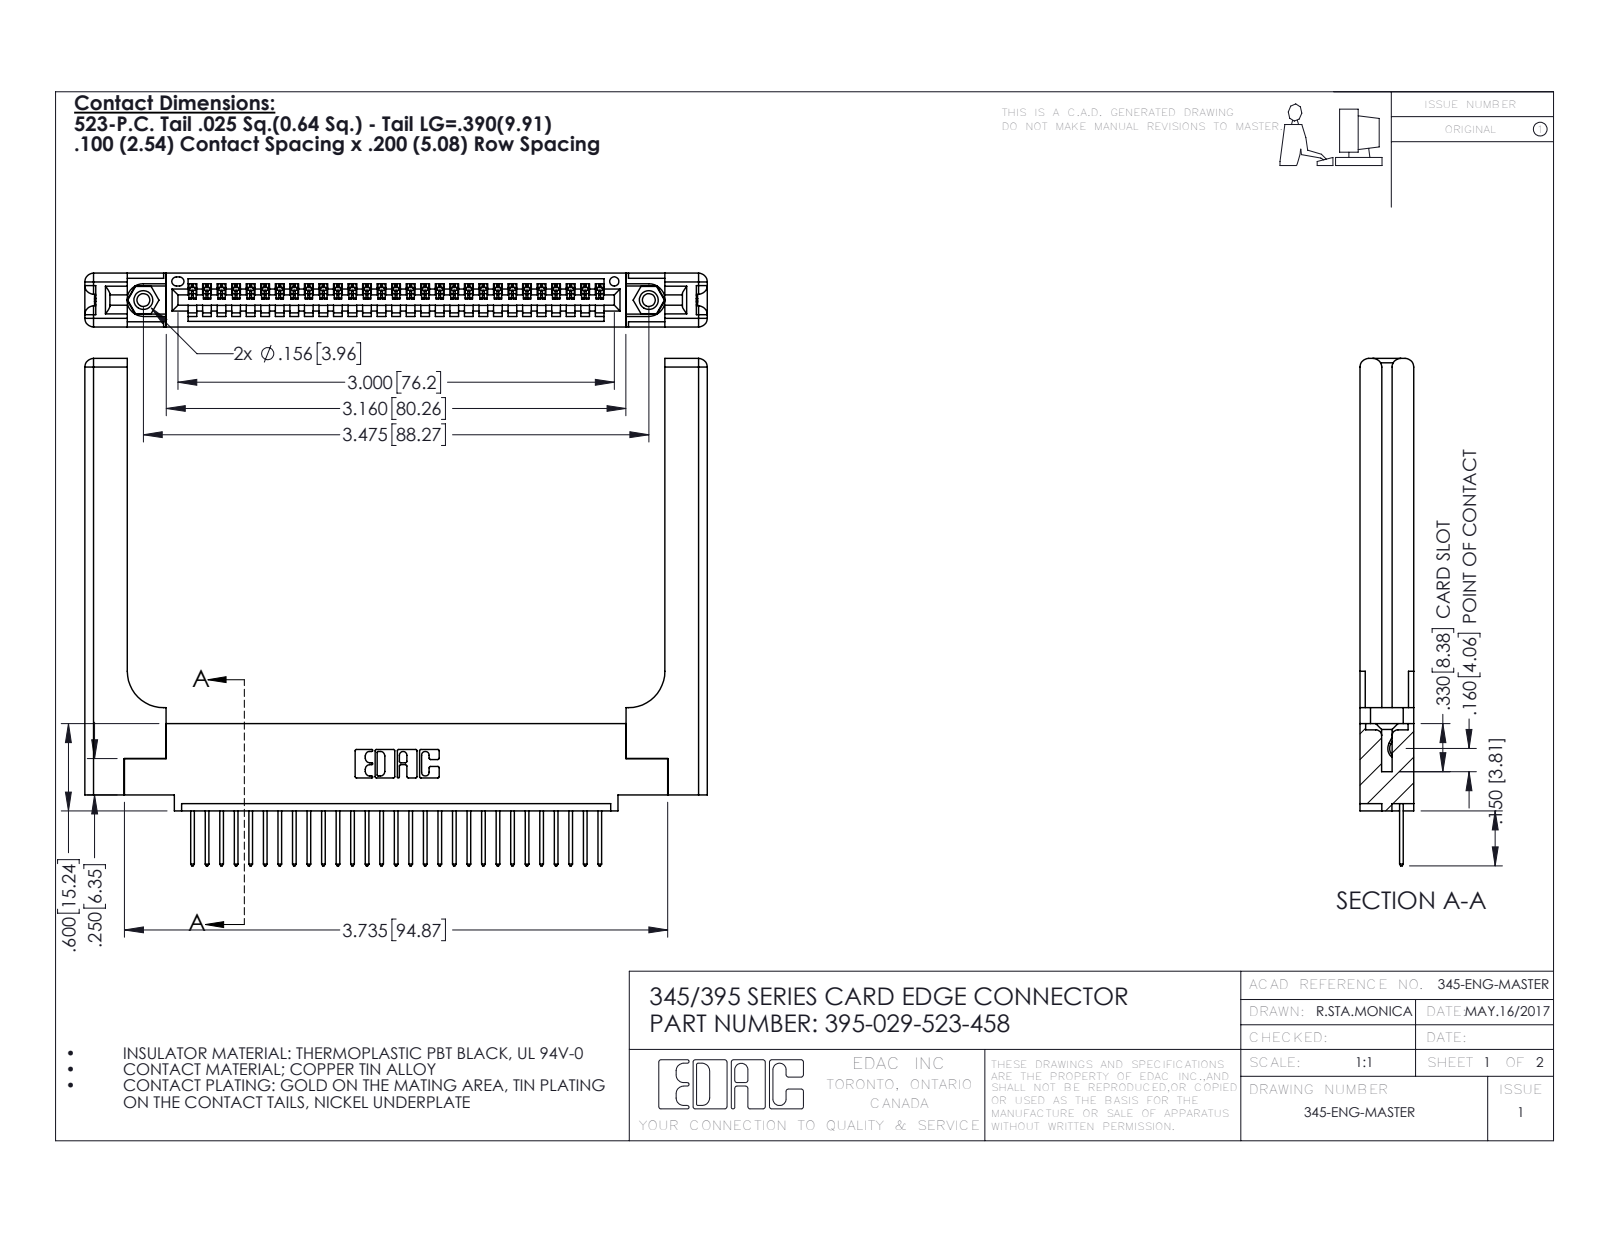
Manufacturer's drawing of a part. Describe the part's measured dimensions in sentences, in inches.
The part is named "345-250-001_345-250-001-102; 345-292-001_345-293-123; 395-029-523-458; 345-220-058_345-220-058 (+1 more)". Its 3-D file was written by "SolidWorks 2016 (CONFIG_CONTROL_DESIGN)". It is 34 solids with 2068 faces: 1392 planar, 616 cylindrical and 60 other. Overall it measures 4.279 by 3.487 by 0.37 inches. Its volume is 1.137 cubic inches and its surface area 29 square inches. Round holes: 2 of diameter 0.089, 2 of diameter 0.125, 2 of diameter 0.156, 1 of diameter 0.064. Round bosses or shafts: 2 of diameter 0.155. Partial cylindrical surfaces (rounded edges, fillets, slot ends): 58 of radius 0.006, 58 of radius 0.01, 22 of radius 0.01, 16 of radius 0.06, 6 of radius 0.007, 6 of radius 0.031, 3 of radius 0.026, 2 of radius 0.03. The main face-to-face distances are 0.37, 0.072, 0.298, 0.098, 0.272, 0.025, 0.2, 0.148, 0.15, 0.077. The hole center spacings are 0.27, 3.24, 3.475.
